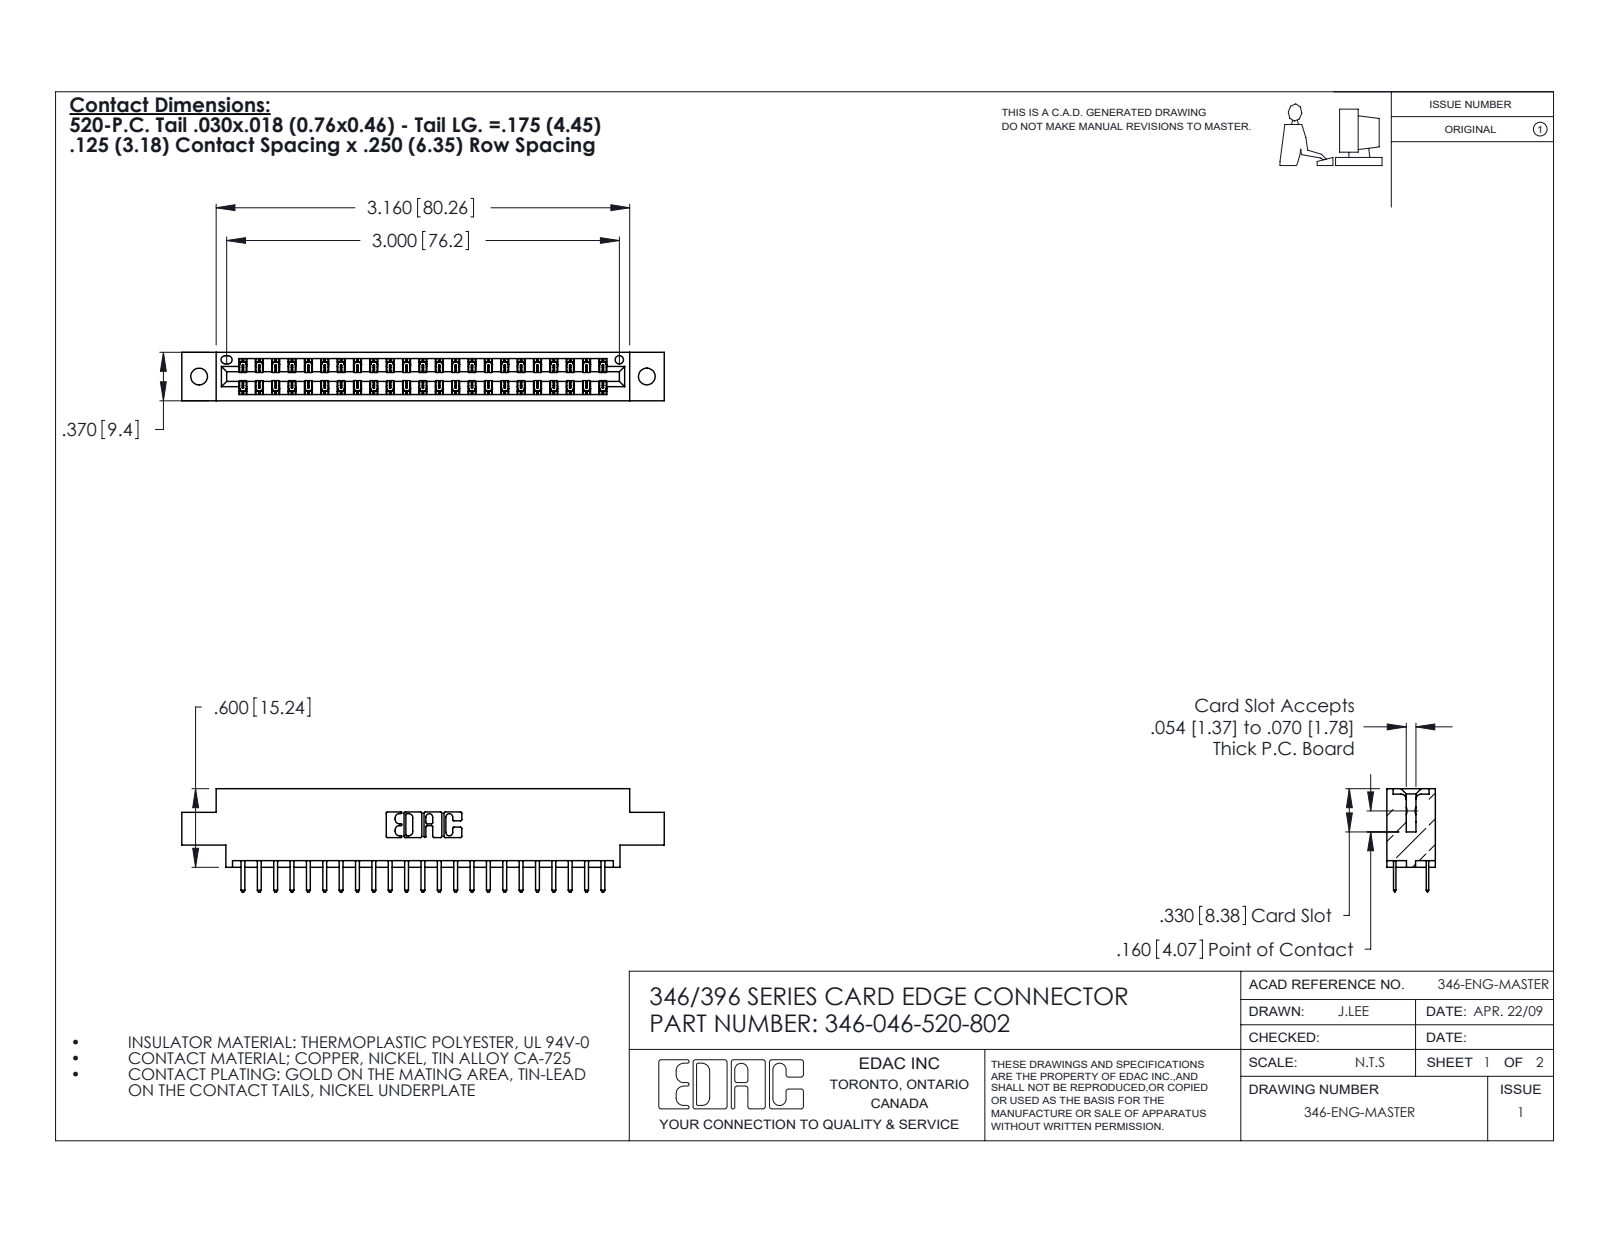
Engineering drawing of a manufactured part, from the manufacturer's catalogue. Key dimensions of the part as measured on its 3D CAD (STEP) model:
Part name (STEP PRODUCT): 345-292-001_345-293-120; 346-046-520-802; 346 Part_0.170 Offset - 0.128 Dia
STEP written by: SolidWorks 2020 (CONFIG_CONTROL_DESIGN)
Units: inches
Bodies: 47 solids, 2702 faces (1782 planar, 920 cylindrical, 0 other)
Overall size (bounding box): 3.685 × 0.788 × 0.37
Volume: 0.535 in³ · Surface area: 18.01 in²
Round holes (diameter × count): ⌀0.128 ×2, ⌀0.064 ×1
Partial cylindrical surfaces — rounded edges, fillets, slot ends (radius × count): R0.006 ×69, R0.01 ×50, R0.01 ×22, R0.007 ×6, R0.031 ×6, R0.026 ×3, R0.014 ×2, R0.022 ×2
Main face-to-face distances: 0.048, 0.322, 0.25, 0.37, 0.275, 0.072, 0.298, 0.025, 0.148, 0.222
Hole centre spacings: 0.246, 3.212, 3.42
